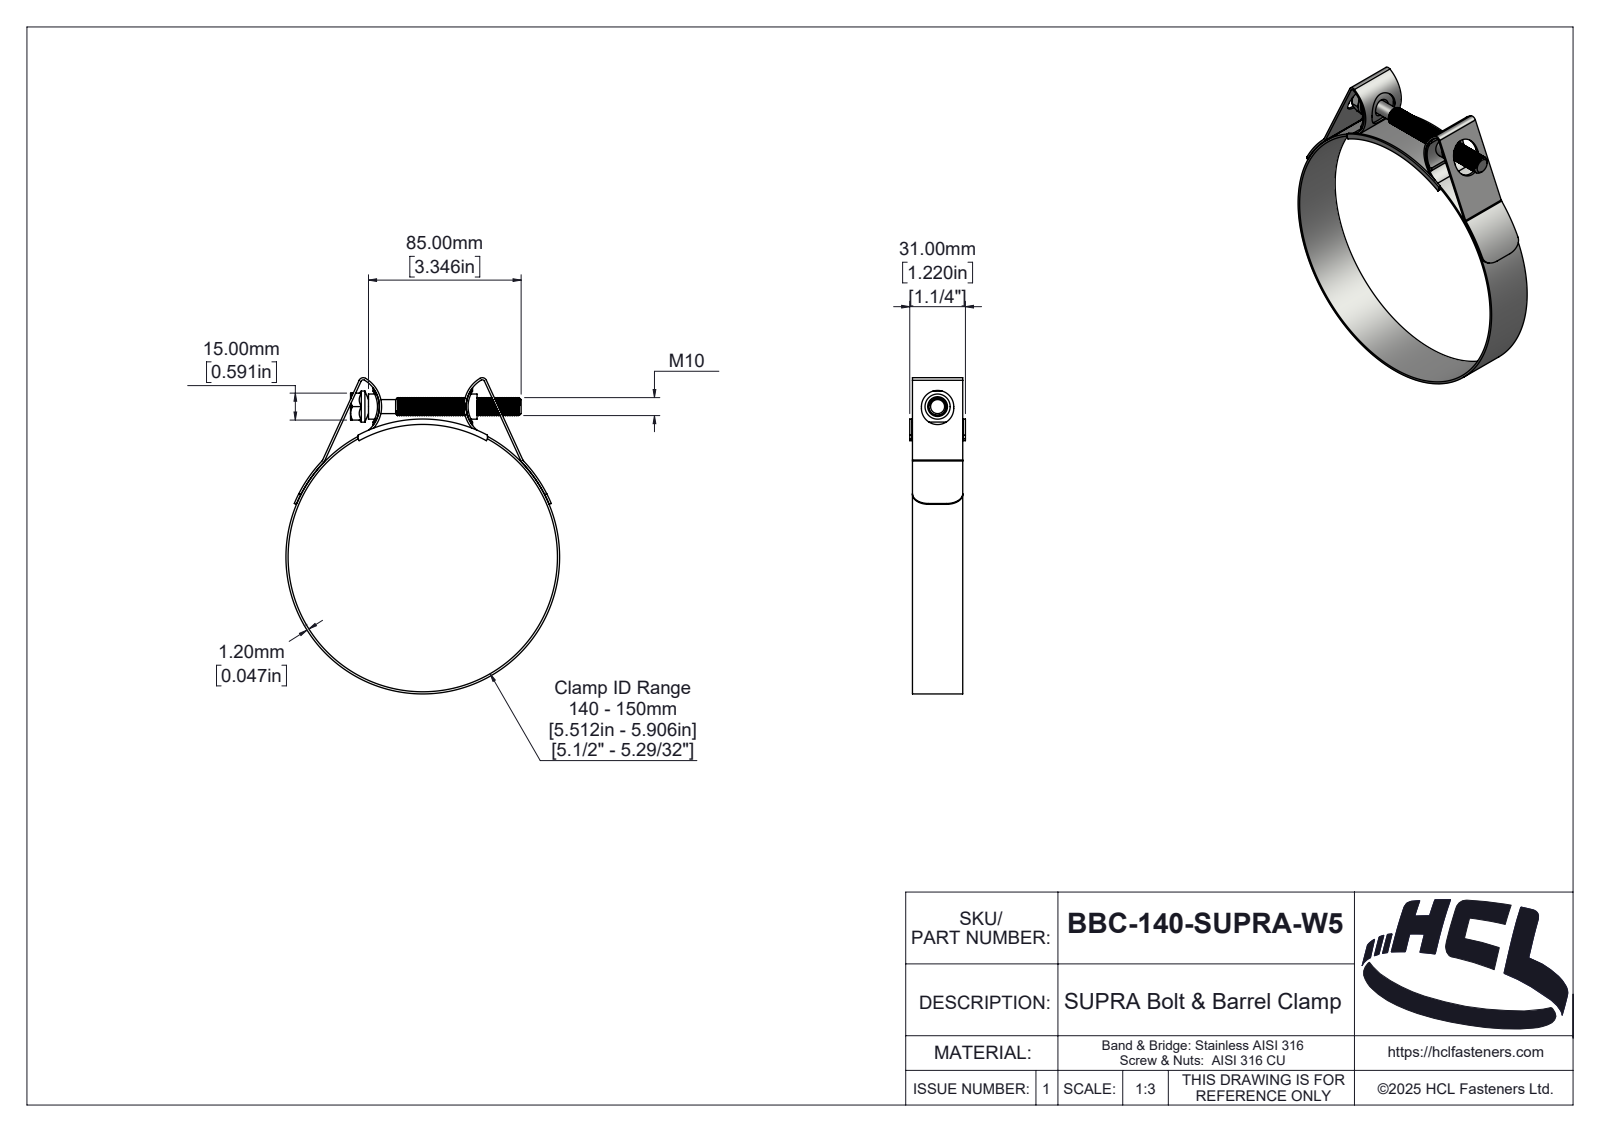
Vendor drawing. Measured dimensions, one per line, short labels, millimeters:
name: BBC-140-SUPRA-W5
written by: SolidWorks 2025 (AUTOMOTIVE_DESIGN)
unit: mm
bodies: 5 solids, 380 faces (46 planar, 248 cylindrical, 86 other)
size: 176.02 × 152.4 × 31
volume: 32 481 mm³; area: 48 473 mm²
holes: 1× ⌀150
bosses: 1× ⌀152.4, 1× ⌀17.32, 1× ⌀14, 1× ⌀10, 1× ⌀7.8
rounds: 4× R1, 2× R1.3, 2× R2, 2× R2.5, 2× R3.2, 2× R9, 2× R16.03, 2× R17.03
face distances: 1.2, 28, 1.5, 29.5, 29.8, 28.3, 31, 28.6, 15, 2.5
